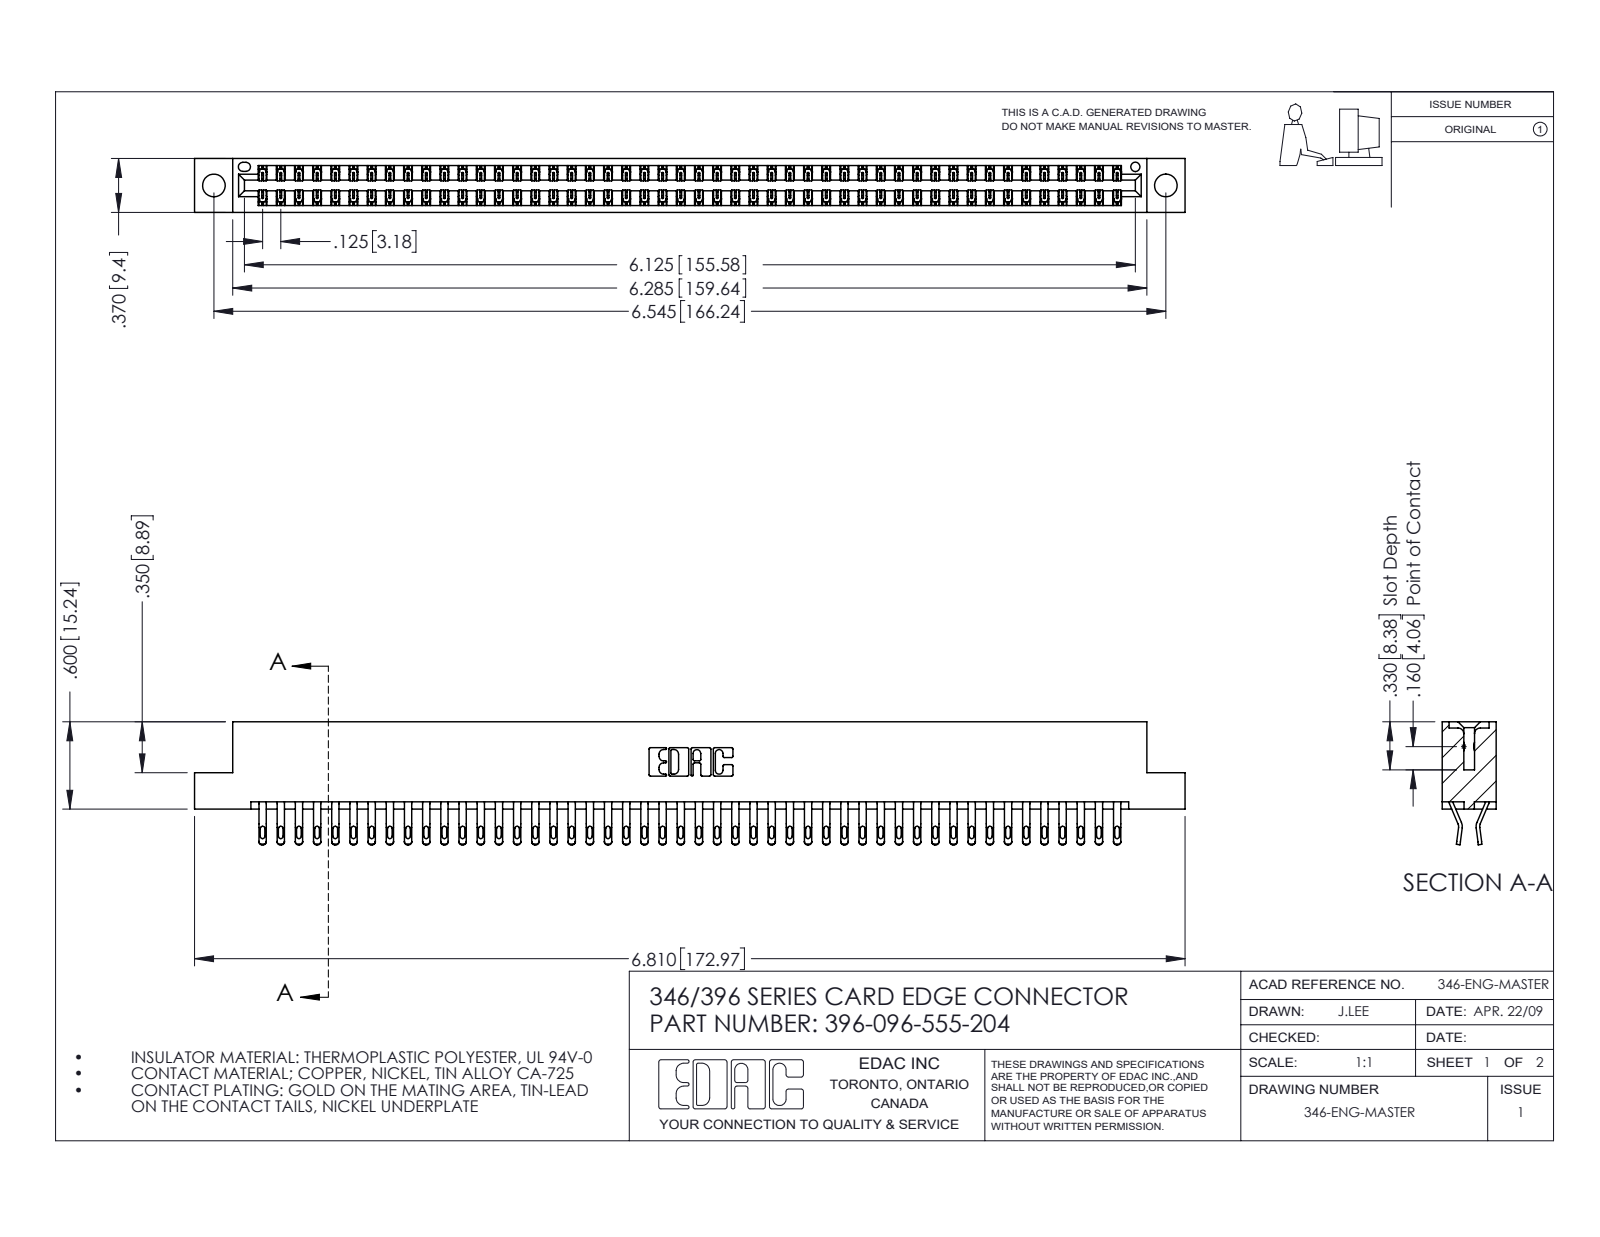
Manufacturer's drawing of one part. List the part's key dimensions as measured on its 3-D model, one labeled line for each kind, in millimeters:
Part name (STEP PRODUCT): 396-096-555-204; 346 Part_Flush Mounting Lugs - 0.156 Dia-TH; 345-292-001_555 Tail
STEP written by: SolidWorks 2016 (CONFIG_CONTROL_DESIGN)
Units: millimetres
Bodies: 97 solids, 5690 faces (3244 planar, 2446 cylindrical, 0 other)
Overall size (bounding box): 173 × 21.5 × 9.4
Volume: 17 110 mm³ · Surface area: 24 410 mm²
Round holes (diameter × count): ⌀4 ×2, ⌀1.6 ×1
Partial cylindrical surfaces — rounded edges, fillets, slot ends (radius × count): R0.4 ×192, R0.5 ×192, R0.2 ×144, R0.3 ×22, R0.2 ×6, R0.8 ×6, R0.7 ×3, R0.3 ×2
Main face-to-face distances: 1.2, 8.2, 9.4, 6.4, 0.6, 1.8, 7.6, 7, 3.8, 5.6
Hole centre spacings: 6.2, 160.9, 166.2
